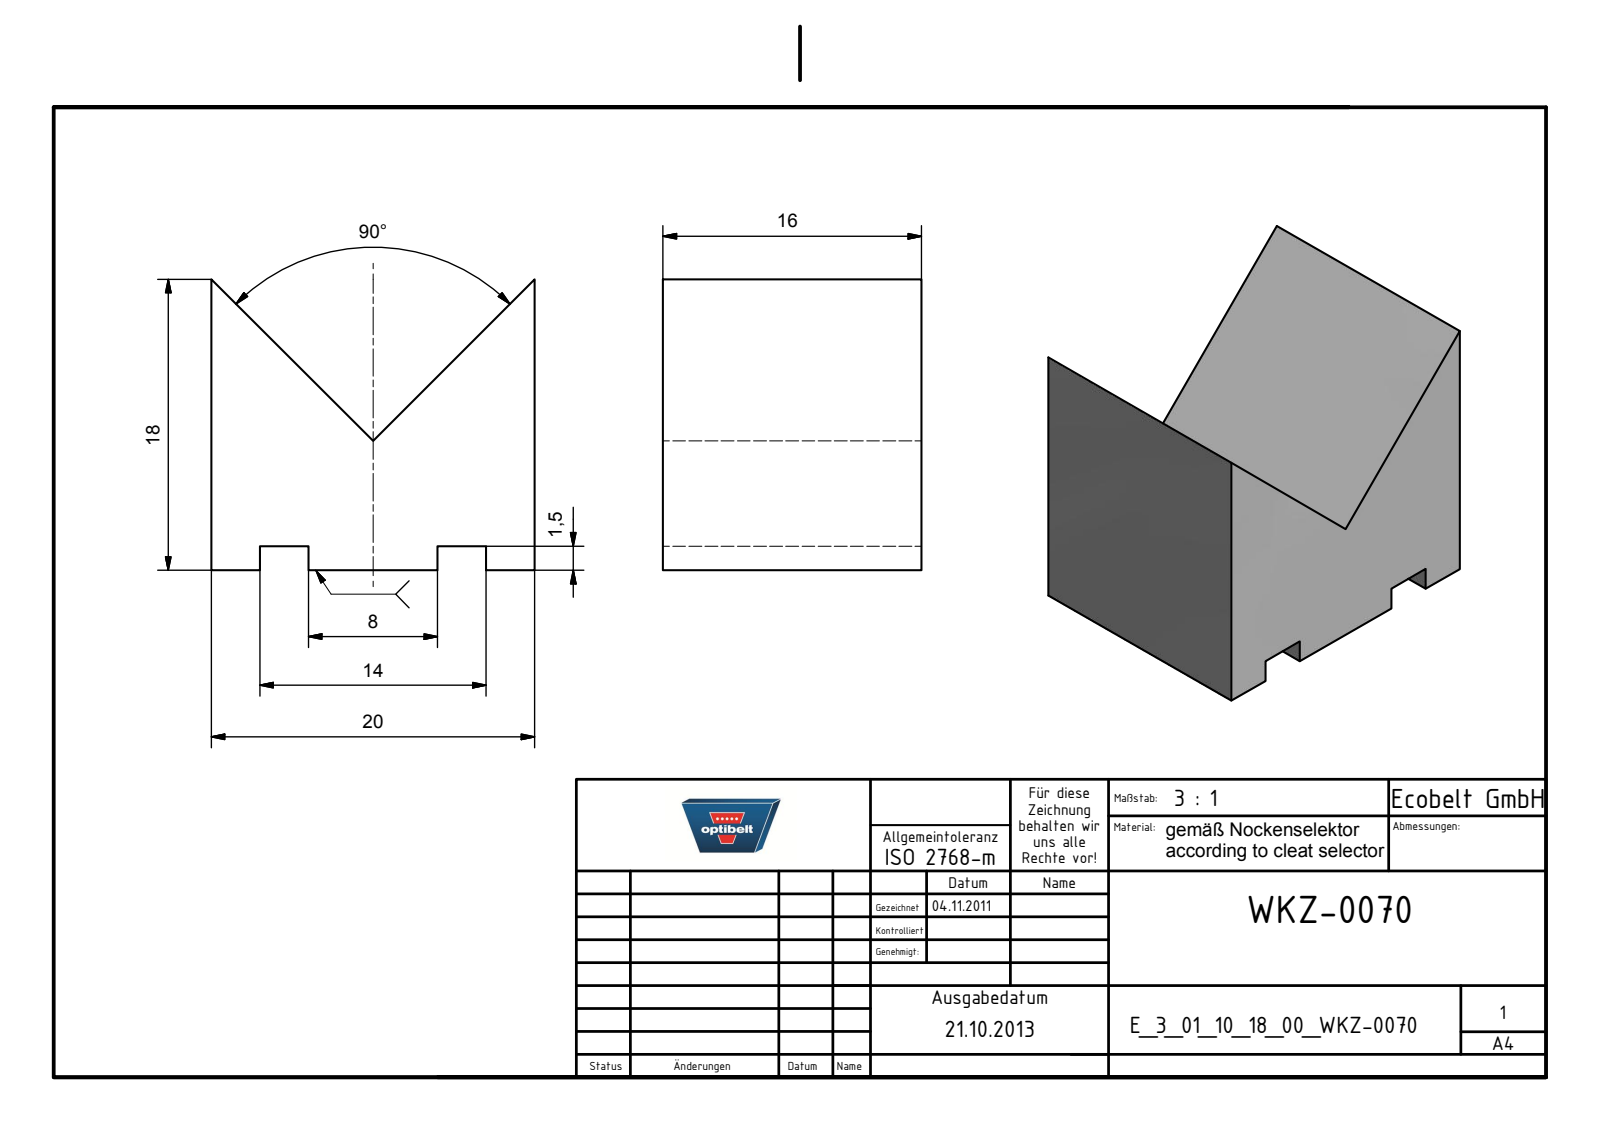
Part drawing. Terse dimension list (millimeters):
name: E_3_01_10_18_00_WKZ-0070
written by: Autodesk Inventor 2025 (AUTOMOTIVE_DESIGN)
unit: mm
bodies: 1 solid, 15 faces (15 planar, 0 cylindrical, 0 other)
size: 20 × 18 × 16
volume: 4 016 mm³; area: 1 947 mm²
face distances: 20, 16, 3, 1.5, 14, 6, 17, 11, 8
